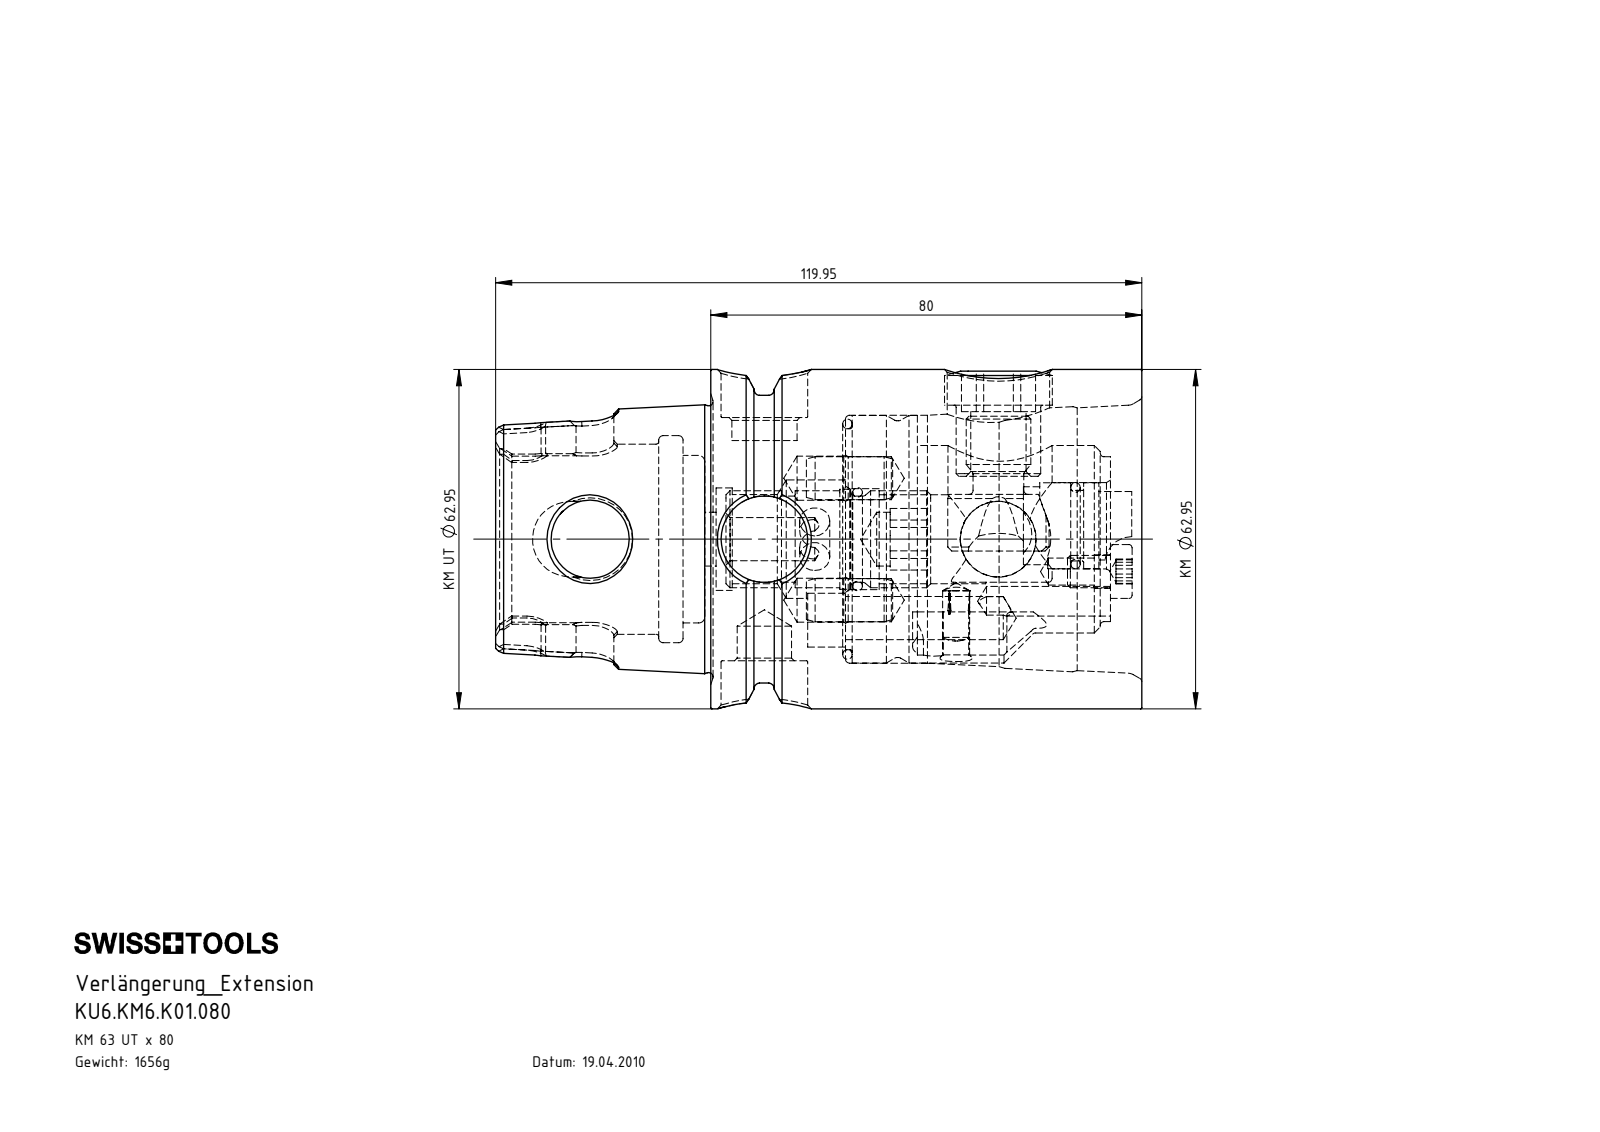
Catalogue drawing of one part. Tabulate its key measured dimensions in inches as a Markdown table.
| quantity | value |
| --- | --- |
| part name | KM6-ER1.001.050_A; KM6-ER1.005.25_A; KM6-ER1.002.019_A; DIN 3771 - 15.6x1.78 (+8 more) |
| STEP written by | SolidWorks 2017 (CONFIG_CONTROL_DESIGN) |
| units | inches |
| bodies | 18 solids, 730 faces (217 planar, 195 cylindrical, 318 other) |
| overall size | 4.722 × 2.478 × 2.478 |
| volume | 13.05 in³ |
| surface area | 111.7 in² |
| round holes (diameter × count) | 0.315 × 6, 0.197 × 4, 0.321 × 4, 0.217 × 3, 0.244 × 2, 0.632 × 2, 0.748 × 2, 0.394 × 1, 0.398 × 1, 0.404 × 1, 0.476 × 1, 0.555 × 1 |
| round bosses / shafts (diameter × count) | 0.394 × 2, 0.236 × 2, 2.478 × 1, 1.808 × 1, 1.73 × 1, 1.614 × 1, 1.369 × 1, 1.205 × 1 |
| partial cylindrical surfaces (radius × count) | 0.157 × 6, 0.016 × 2, 0.156 × 2, 0.25 × 2, 0.277 × 2, 0.278 × 2, 0.315 × 2, 0.177 × 1 |
| main face-to-face distances | 0.984, 2.165, 3.15, 0.228, 0.043, 1.028, 3.193, 2.921, 1.553, 1.51 |
| hole center spacings | 0.63, 0.891, 0.564, 0.171, 0.242, 0.298, 0.327, 0.4 |
